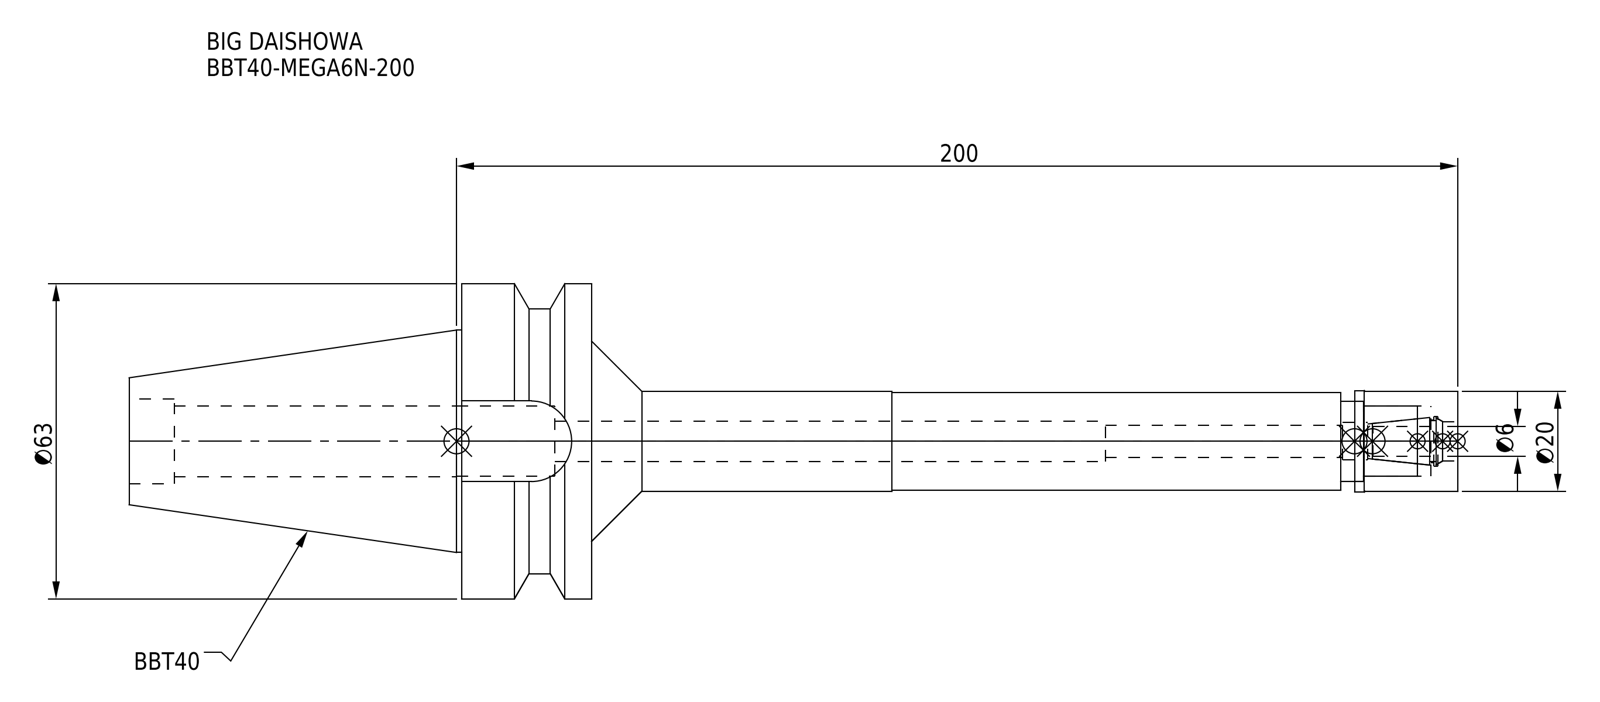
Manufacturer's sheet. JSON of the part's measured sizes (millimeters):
{"part_name": "BBT40-MEGA6N-200_1.stp; BBT40-MEGA6N-200-060-FreeParts; BBT40-MEGA6N-200-060.stp; BBT40-MEGA6N-200 (+3 more)", "step_written_by": "SolidWorks 2019 (CONFIG_CONTROL_DESIGN)", "units": "millimeters", "bodies": {"solids": 2, "faces": 83, "planar": 25, "cylindrical": 44, "other": 14}, "overall_size": [265.4, 63, 63], "volume_mm3": 169954, "surface_area_mm2": 39104, "round_holes": [[6.4, 1], [7.5, 1], [7.9, 1], [8, 1], [8.5, 1], [10, 1], [14, 1], [14.2, 1], [16, 1], [17, 1]], "round_bosses_or_shafts": [[63, 1], [53, 1], [44.45, 1], [20.3, 1], [20, 1], [19.5, 1]], "partial_cylinders_radius": [[8.05, 1]], "face_to_face_distances": [26, 45, 92.4, 66.4, 173, 199, 265.4, 16.1, 152.4, 18.6]}
